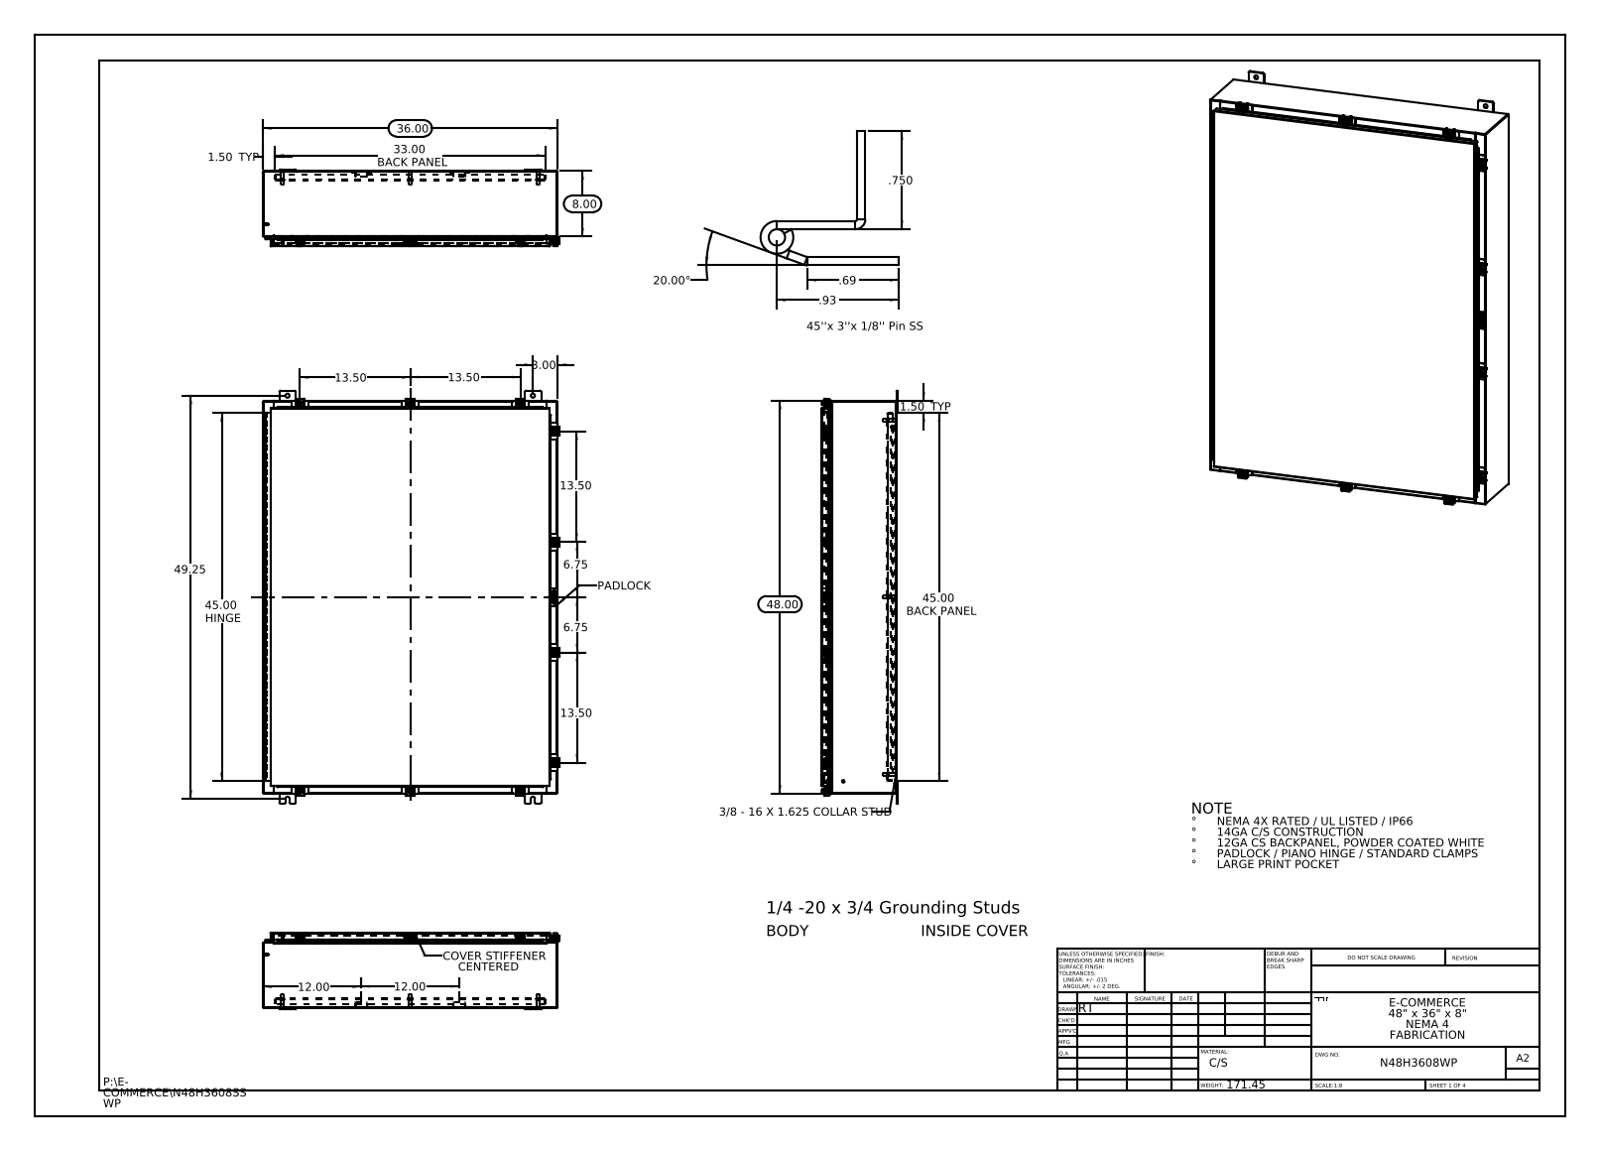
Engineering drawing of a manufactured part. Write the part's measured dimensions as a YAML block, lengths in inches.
part_name: "N48H3608SSWP Enclosure Stiffener; N48H3608SSWP Mounting Feet; N48H3608SSWP 125 Pin Hinge; N48H3608SSWP Clamp Bracket (+8 more)"
step_written_by: "SolidWorks 2013 (CONFIG_CONTROL_DESIGN)"
units: inches
bodies: {solids: 82, faces: 3115, planar: 1586, cylindrical: 1301, other: 228}
overall_size: [50.5, 36.211, 9.389]
volume: 600.9
surface_area: 14920
round_holes:
  - {diameter: 0.5, count: 12}
  - {diameter: 0.213, count: 10}
  - {diameter: 0.26, count: 10}
  - {diameter: 0.25, count: 6}
  - {diameter: 0.125, count: 2}
round_bosses_or_shafts:
  - {diameter: 0.25, count: 11}
  - {diameter: 0.5, count: 10}
  - {diameter: 0.399, count: 10}
  - {diameter: 0.625, count: 8}
  - {diameter: 0.375, count: 8}
  - {diameter: 0.33, count: 8}
  - {diameter: 0.157, count: 6}
  - {diameter: 0.14, count: 6}
partial_cylinders:
  - {radius: 0.06, count: 46}
  - {radius: 0.013, count: 39}
  - {radius: 0.088, count: 33}
  - {radius: 0.19, count: 24}
  - {radius: 0.12, count: 20}
  - {radius: 0.141, count: 20}
  - {radius: 0.05, count: 15}
  - {radius: 0.08, count: 14}
face_to_face_distances: [0.075, 9.126, 9.051, 0.104, 9.201, 1, 8.126, 1.075, 8.051, 1.179]
hole_center_spacings: [13.5, 13.663, 20, 20.123, 21.625, 23.82, 27, 38.003]
